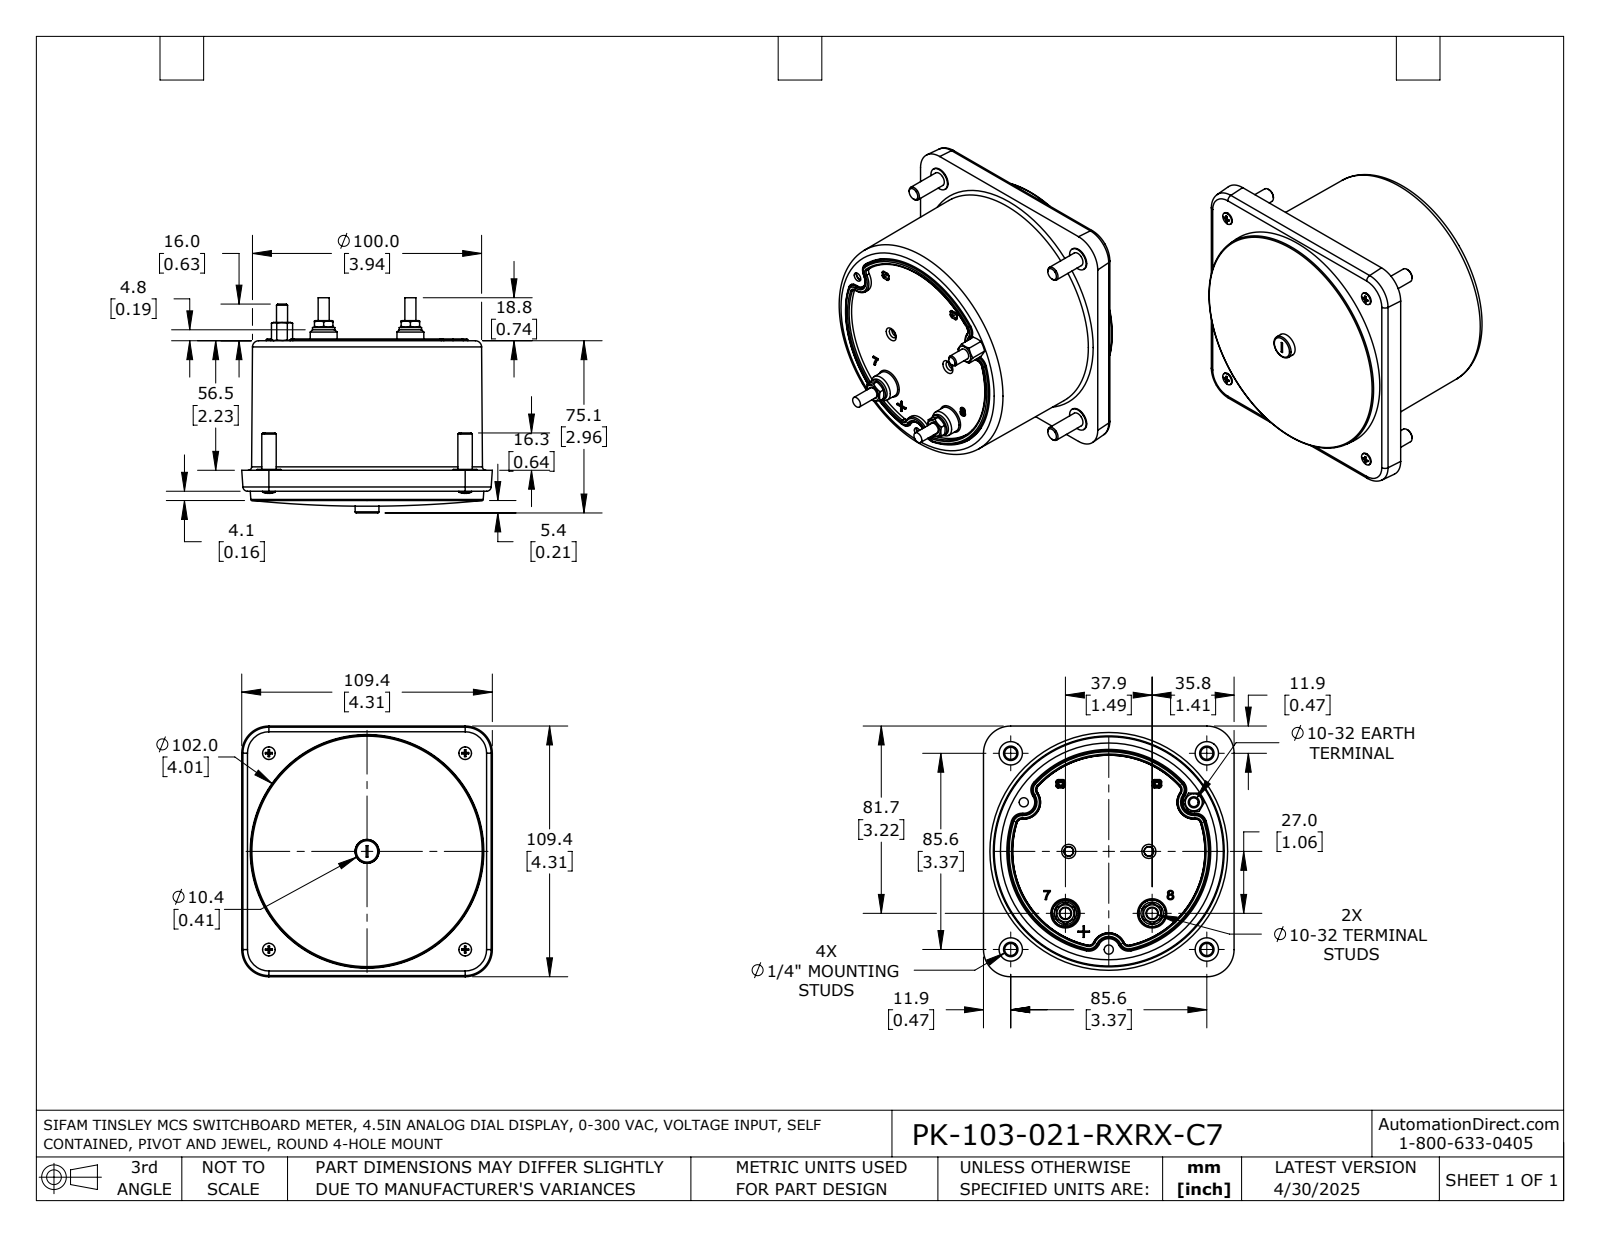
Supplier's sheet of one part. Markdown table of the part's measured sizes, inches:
| quantity | value |
| --- | --- |
| part name | PK-103-021-RXRX-C7 |
| STEP written by | SolidWorks 2021 (AUTOMOTIVE_DESIGN) |
| units | inches |
| bodies | 1 solid, 609 faces (167 planar, 141 cylindrical, 301 other) |
| overall size | 4.307 × 4.307 × 3.697 |
| volume | 36.28 in³ |
| surface area | 82.21 in² |
| round holes (diameter × count) | 0.094 × 4, 0.138 × 4, 0.315 × 4, 0.157 × 3, 0.209 × 2 |
| round bosses / shafts (diameter × count) | 0.402 × 4, 0.248 × 4, 0.217 × 4, 0.114 × 4, 0.19 × 3, 0.384 × 2, 0.146 × 1 |
| partial cylindrical surfaces (radius × count) | 0.02 × 24, 0.189 × 9, 0.079 × 4, 1.752 × 1 |
| main face-to-face distances | 2.177, 2.537, 0.36, 0.048, 2.225, 2.585, 0.489, 2.715, 2.667, 0.129 |
| hole center spacings | 3.372, 3.37, 3.374, 3.378, 3.38, 4.769, 0.971, 1.126 |
